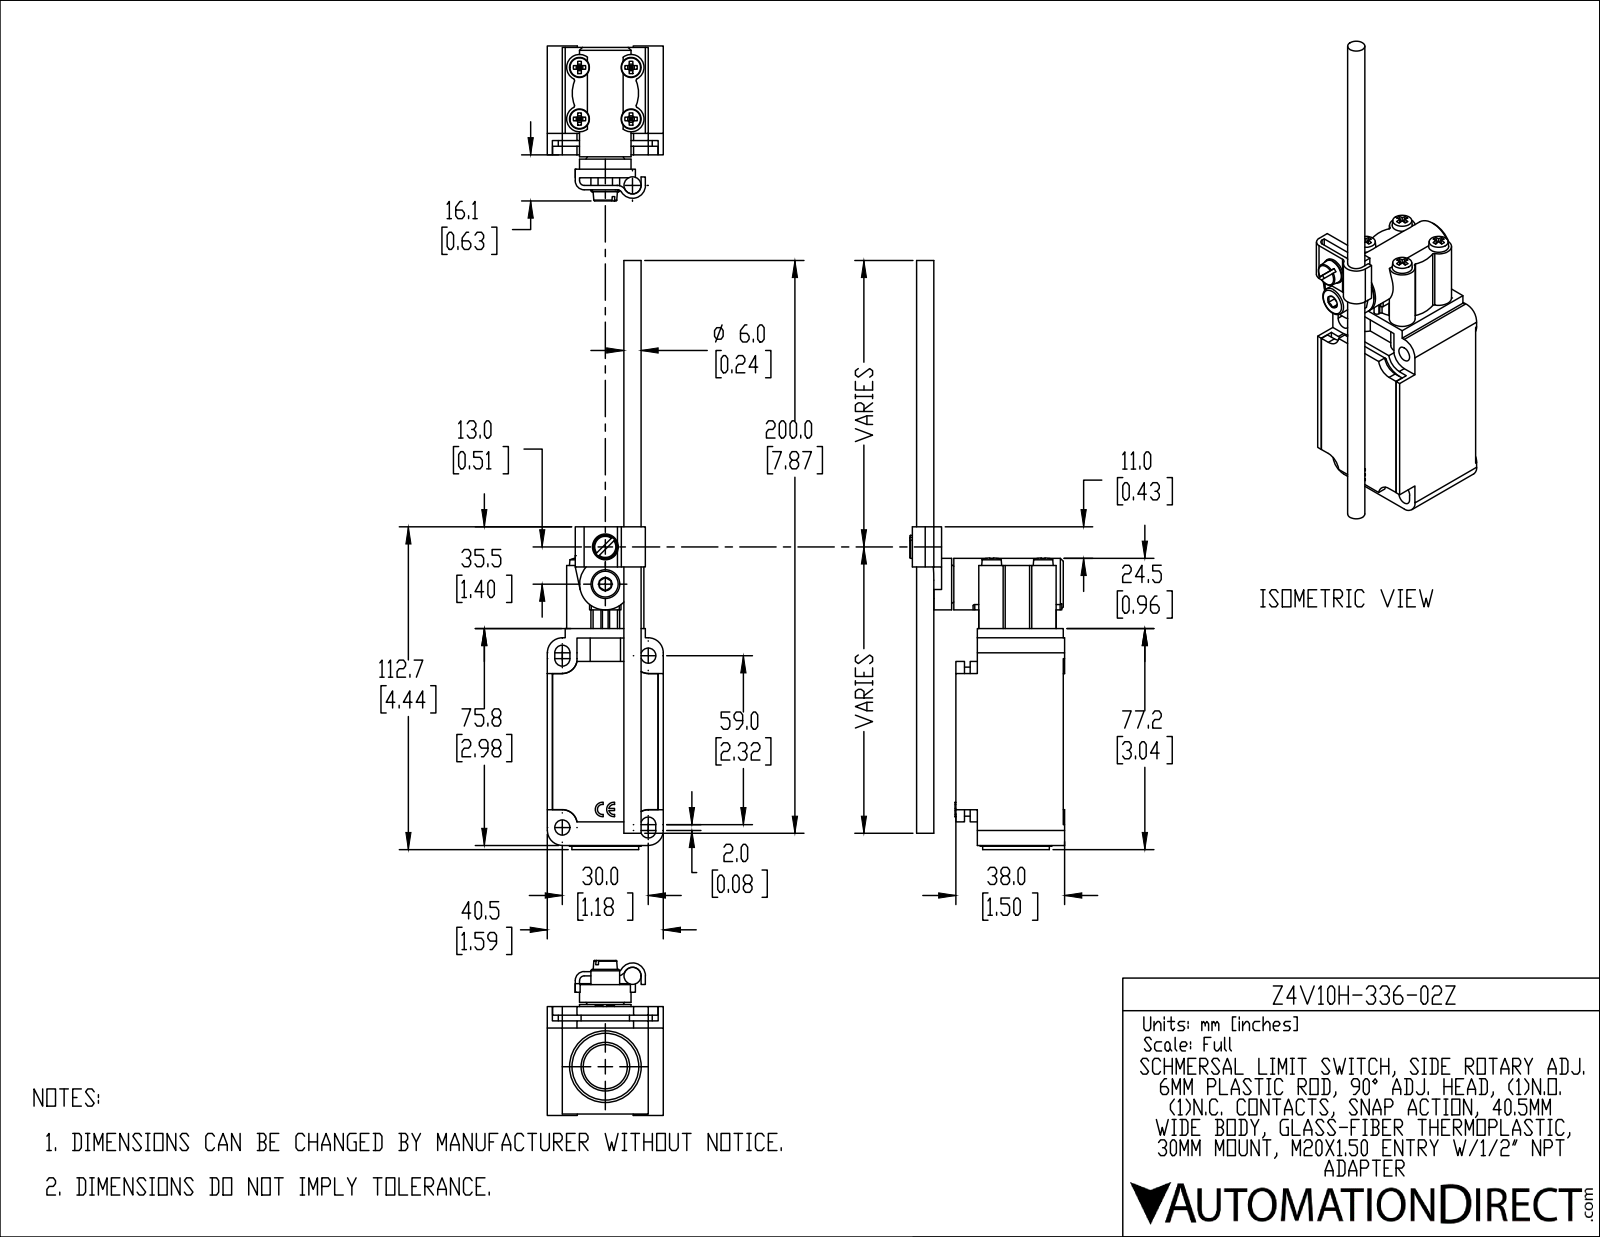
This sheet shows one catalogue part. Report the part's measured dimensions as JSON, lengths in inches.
{"part_name": "Z4V10H-336-02Z", "step_written_by": "SolidWorks 2019 (CONFIG_CONTROL_DESIGN)", "units": "inches", "bodies": {"solids": 4, "faces": 255, "planar": 122, "cylindrical": 111, "other": 22}, "overall_size": [8.098, 2.13, 1.594], "volume_in3": 8.113, "surface_area_in2": 49.21, "round_holes": [[0.209, 2], [0.65, 1], [0.669, 1]], "round_bosses_or_shafts": [[0.984, 1], [0.917, 1], [0.709, 1], [0.394, 1], [0.354, 1], [0.236, 1], [0.197, 1]], "partial_cylinders_radius": [[0.024, 16], [0.205, 8], [0.207, 8], [0.177, 5], [0.104, 4], [0.283, 4], [0.039, 2], [0.063, 2]], "face_to_face_distances": [1.594, 1.476, 0.197, 0.177, 0.315, 1.181, 0.295, 0.118, 0.079, 0.866], "hole_center_spacings": [1.148, 2.641, 3.398]}
